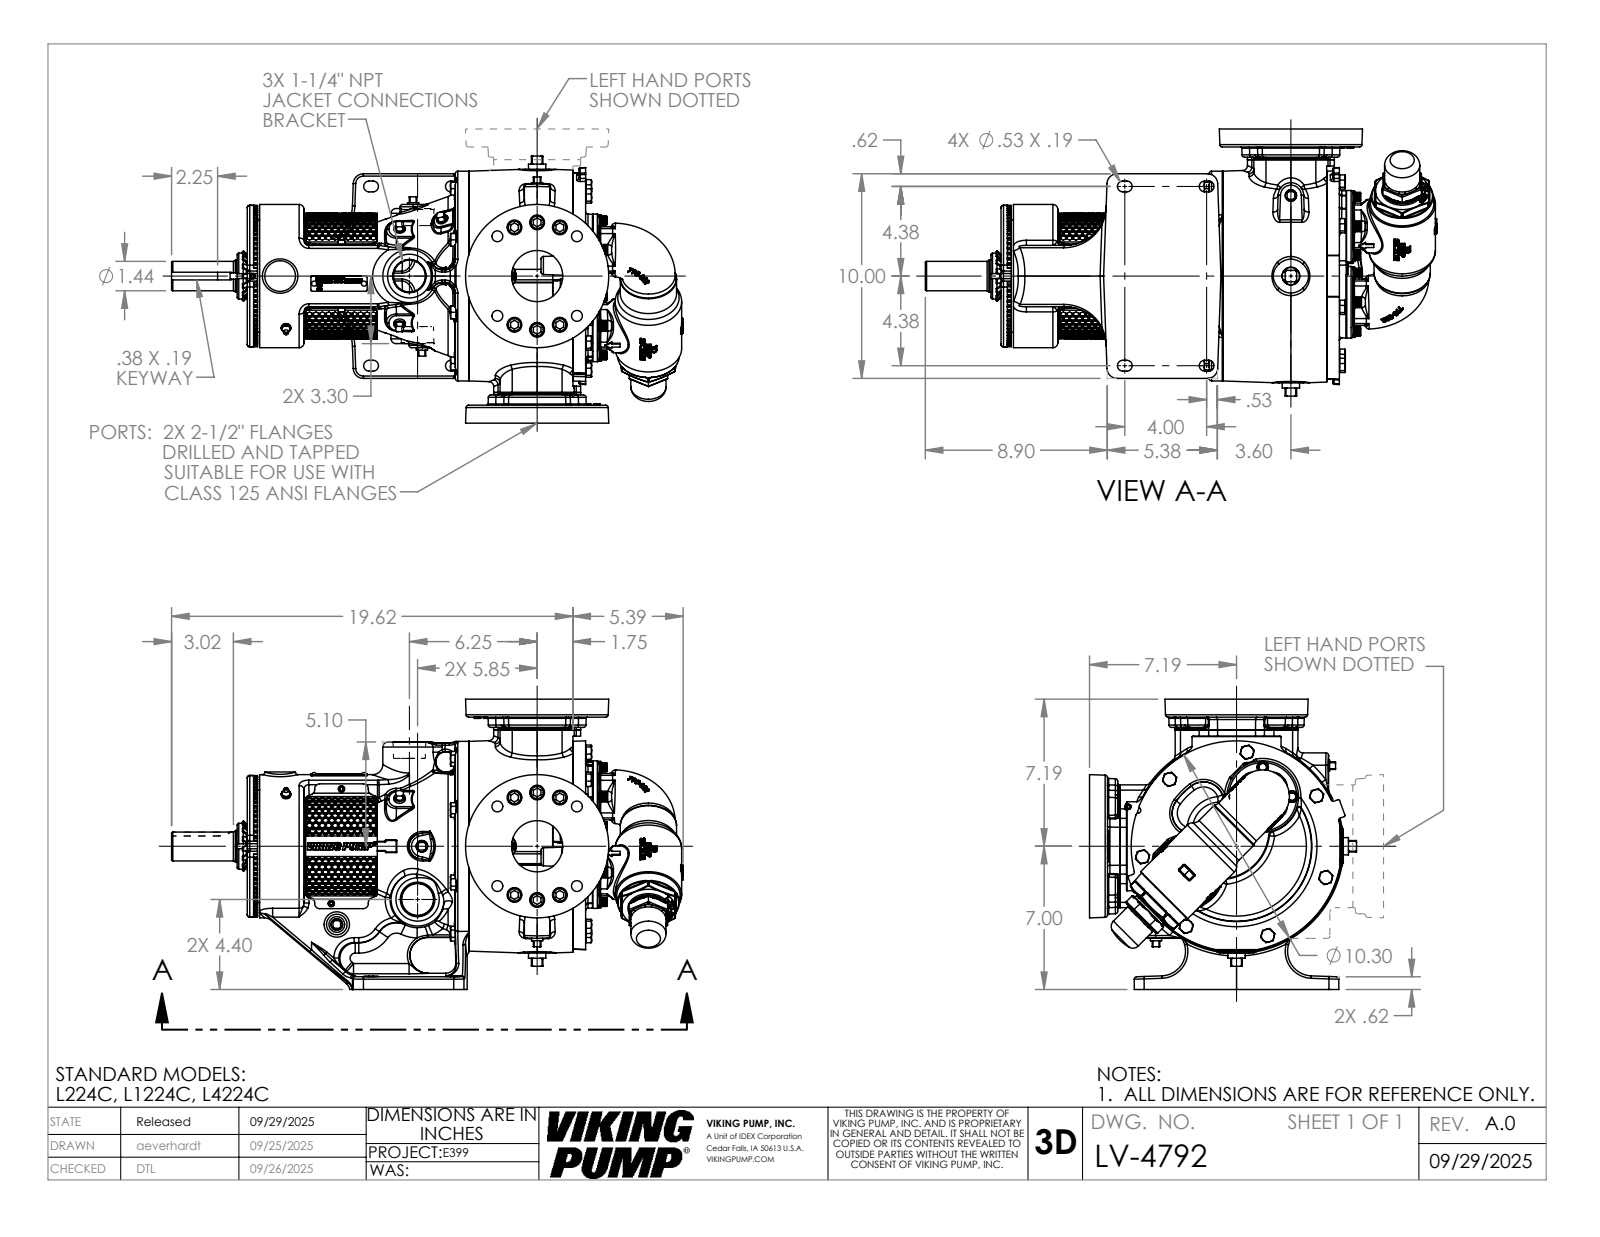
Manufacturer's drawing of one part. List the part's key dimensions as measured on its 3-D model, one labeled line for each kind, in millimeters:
Part name (STEP PRODUCT): LV-4792
STEP written by: SolidWorks 2024 (AUTOMOTIVE_DESIGN)
Units: millimetres
Bodies: 1 solid, 6353 faces (1922 planar, 1169 cylindrical, 3262 other)
Overall size (bounding box): 635.3 × 360.4 × 331.5
Volume: 17 670 000 mm³ · Surface area: 943 900 mm²
Round holes (diameter × count): ⌀18.3 ×12, ⌀13.5 ×8, ⌀27.8 ×8, ⌀5.1 ×6, ⌀6.4 ×6, ⌀4 ×3, ⌀6.8 ×2, ⌀8 ×2, ⌀63.5 ×2, ⌀11.5 ×1, ⌀39.4 ×1, ⌀40.1 ×1
Round bosses / shafts (diameter × count): ⌀16.8 ×12, ⌀15.9 ×9, ⌀14.3 ×8, ⌀15.9 ×6, ⌀88.9 ×3, ⌀11.1 ×3, ⌀7.9 ×3, ⌀260.4 ×1
Partial cylindrical surfaces — rounded edges, fillets, slot ends (radius × count): R1.6 ×109, R1.8 ×74, R3 ×60, R0.8 ×36, R0.3 ×34, R0.2 ×28, R12.7 ×26, R1.5 ×16
Main face-to-face distances: 360.3, 350.3, 57.2, 12.7, 89.8, 260.5, 69.9, 22.4, 15.7, 54.4
Hole centre spacings: 76.2, 69.9, 34.9, 66.7, 23.9, 28.9, 52.3, 55.4
